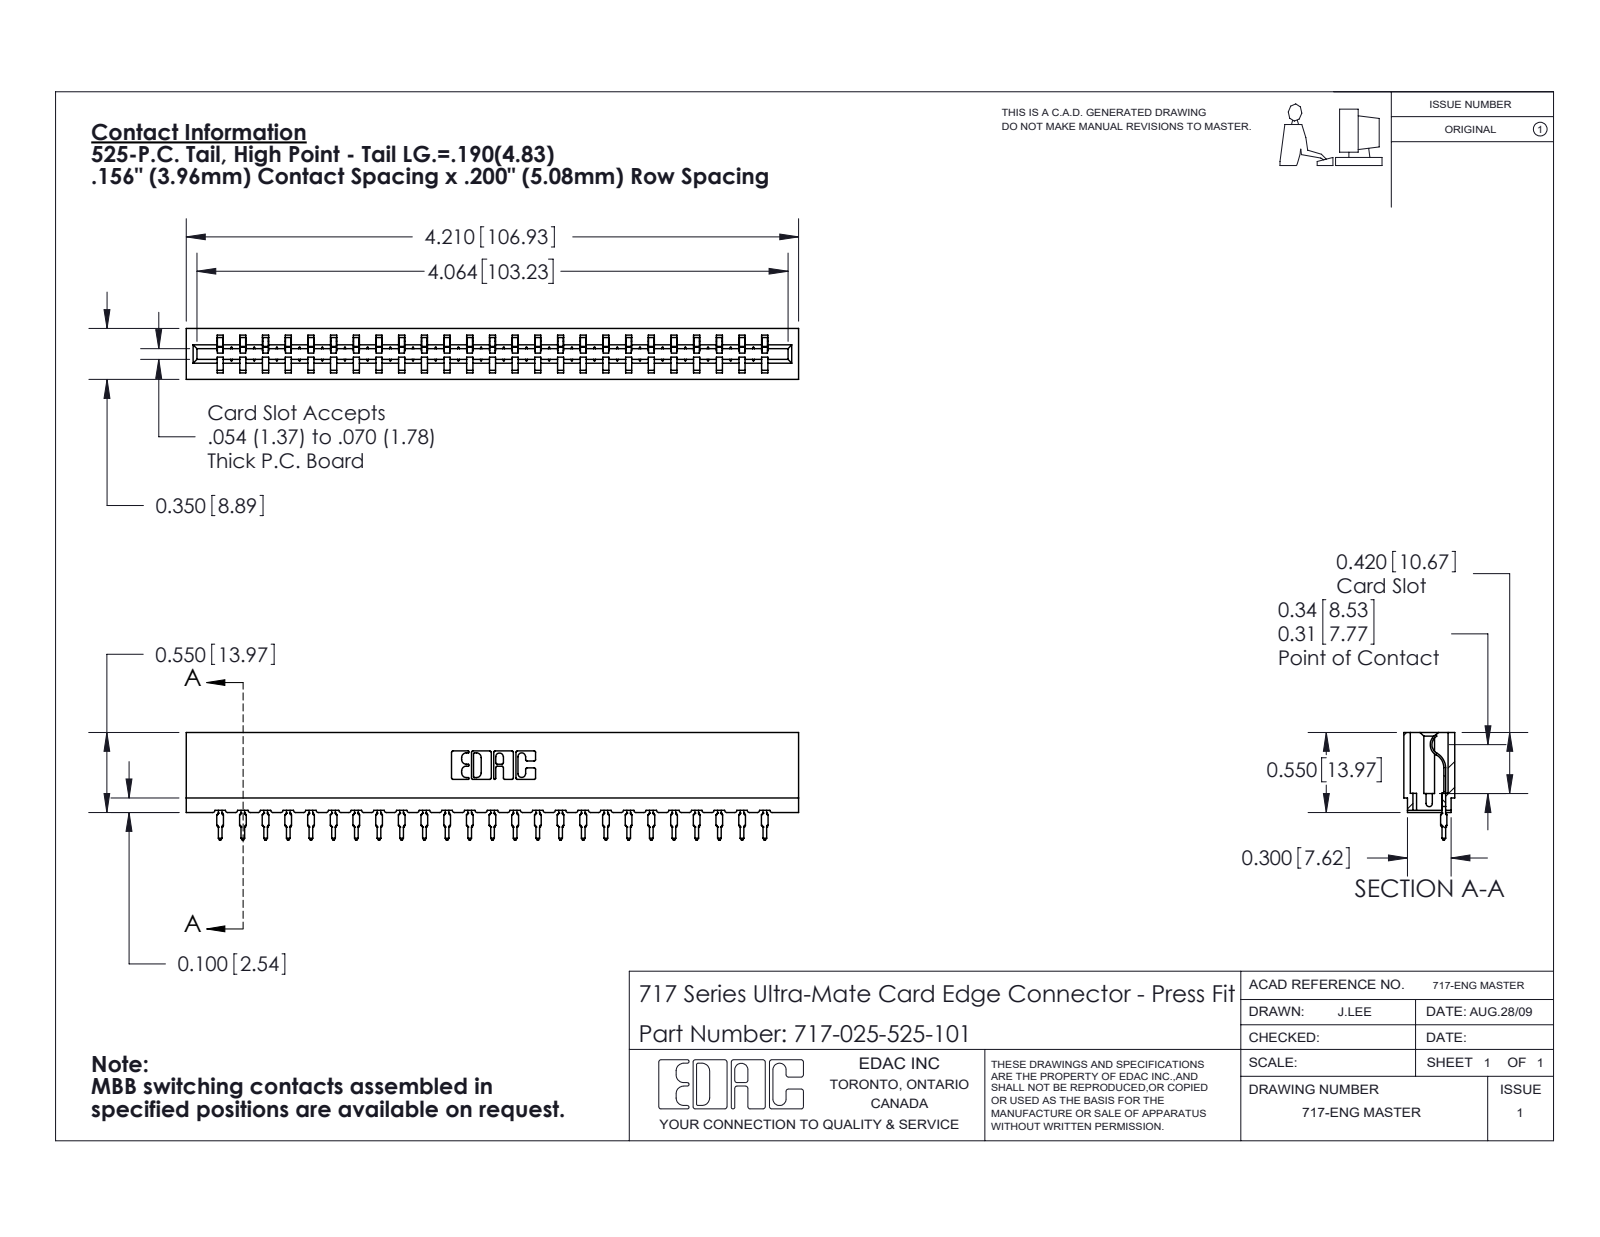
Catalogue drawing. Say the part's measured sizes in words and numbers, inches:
The part is named "717 Part_Insulator Option - 06; 717-025-525-101; 745-292-001_525". Its 3-D file was written by "SolidWorks 2020 (CONFIG_CONTROL_DESIGN)". It is 26 solids with 2919 faces: 1754 planar, 515 cylindrical and 650 other. Overall it measures 4.21 by 0.739 by 0.35 inches. Its volume is 0.554 cubic inches and its surface area 19.38 square inches. Partial cylindrical surfaces (rounded edges, fillets, slot ends): 50 of radius 0.015, 50 of radius 0.021, 22 of radius 0.01, 6 of radius 0.007, 6 of radius 0.031, 4 of radius 0.005, 4 of radius 0.011, 3 of radius 0.026. The main face-to-face distances are 0.212, 0.138, 0.35, 0.156, 0.074, 0.624, 0.045, 0.305, 0.093, 0.167.
